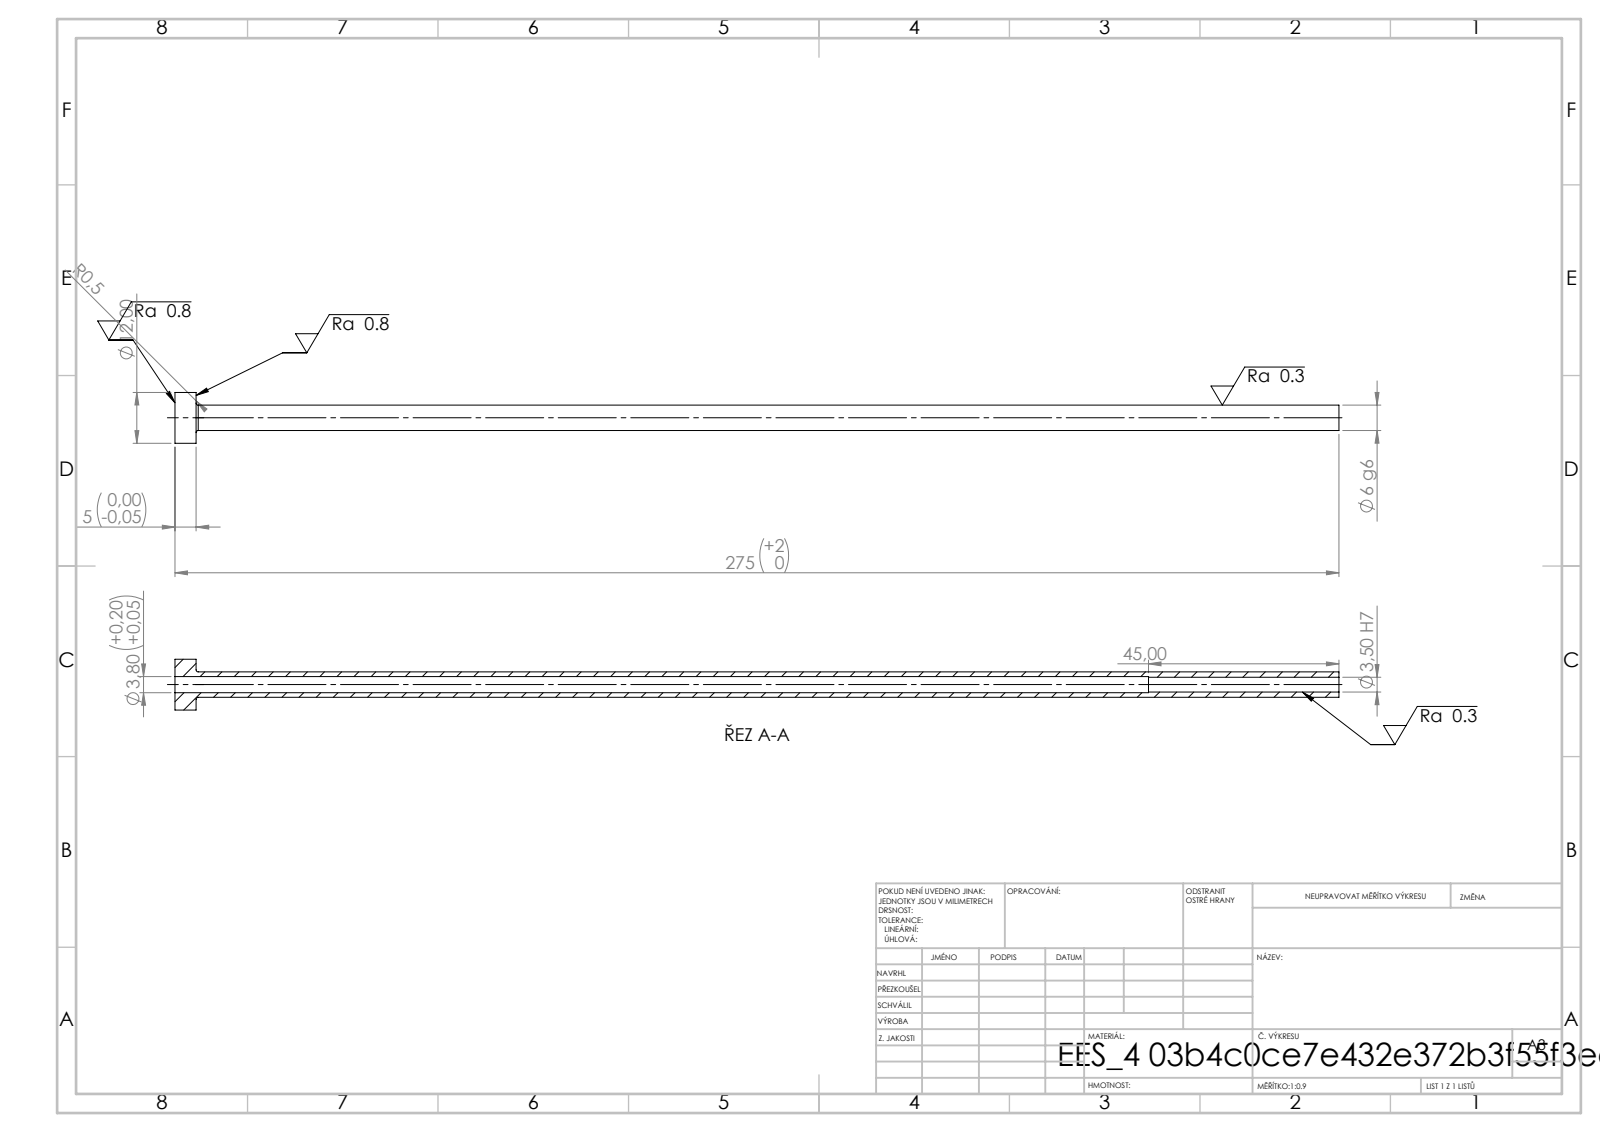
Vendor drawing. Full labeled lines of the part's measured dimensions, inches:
STEP written by: SolidWorks 2019 (CONFIG_CONTROL_DESIGN)
Units: inches
Bodies: 1 solid, 14 faces (4 planar, 8 cylindrical, 2 other)
Overall size (bounding box): 10.827 × 0.472 × 0.472
Volume: 0.315 in³ · Surface area: 13.52 in²
Round holes (diameter × count): ⌀0.138 ×1, ⌀0.15 ×1
Round bosses / shafts (diameter × count): ⌀0.472 ×1, ⌀0.236 ×1
Main face-to-face distances: 0.197, 10.827, 10.63, 9.055, 8.858, 1.772
